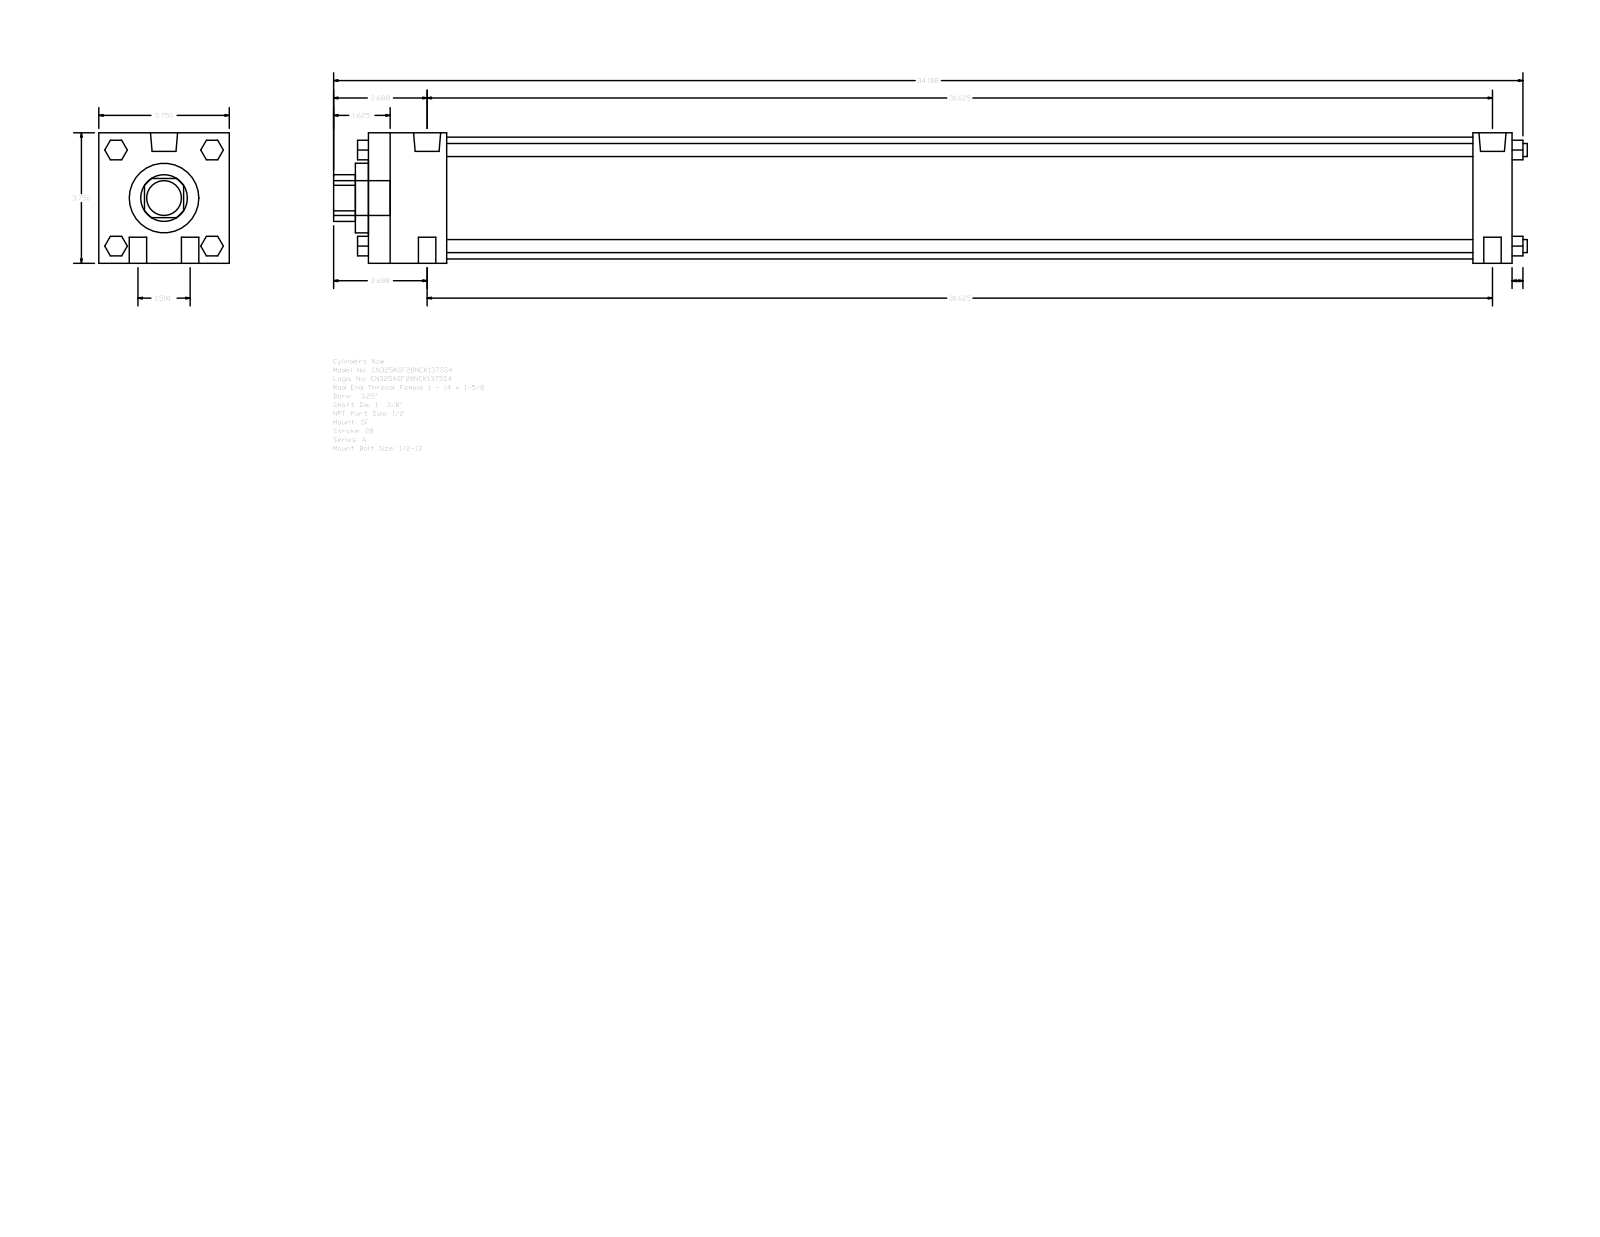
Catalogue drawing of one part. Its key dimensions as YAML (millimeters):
part_name: "A_SF__0325_1.375"
step_written_by: "GSSL Pune (CONFIG_CONTROL_DESIGN)"
units: millimeters
bodies: {solids: 0, faces: 124, planar: 94, cylindrical: 30, other: 0}
overall_size: [871.54, 95.25, 95.25]
round_holes:
  - {diameter: 34.92, count: 1}
  - {diameter: 50.8, count: 1}
  - {diameter: 88.9, count: 1}
round_bosses_or_shafts:
  - {diameter: 12.7, count: 4}
  - {diameter: 9.53, count: 4}
  - {diameter: 19.77, count: 2}
  - {diameter: 8.73, count: 2}
  - {diameter: 25.4, count: 1}
partial_cylinders:
  - {radius: 17.06, count: 1}
face_to_face_distances: [95.24, 835.02, 28.57, 806.45, 57.15, 749.3, 777.87, 9.52, 66.67, 815.97]
